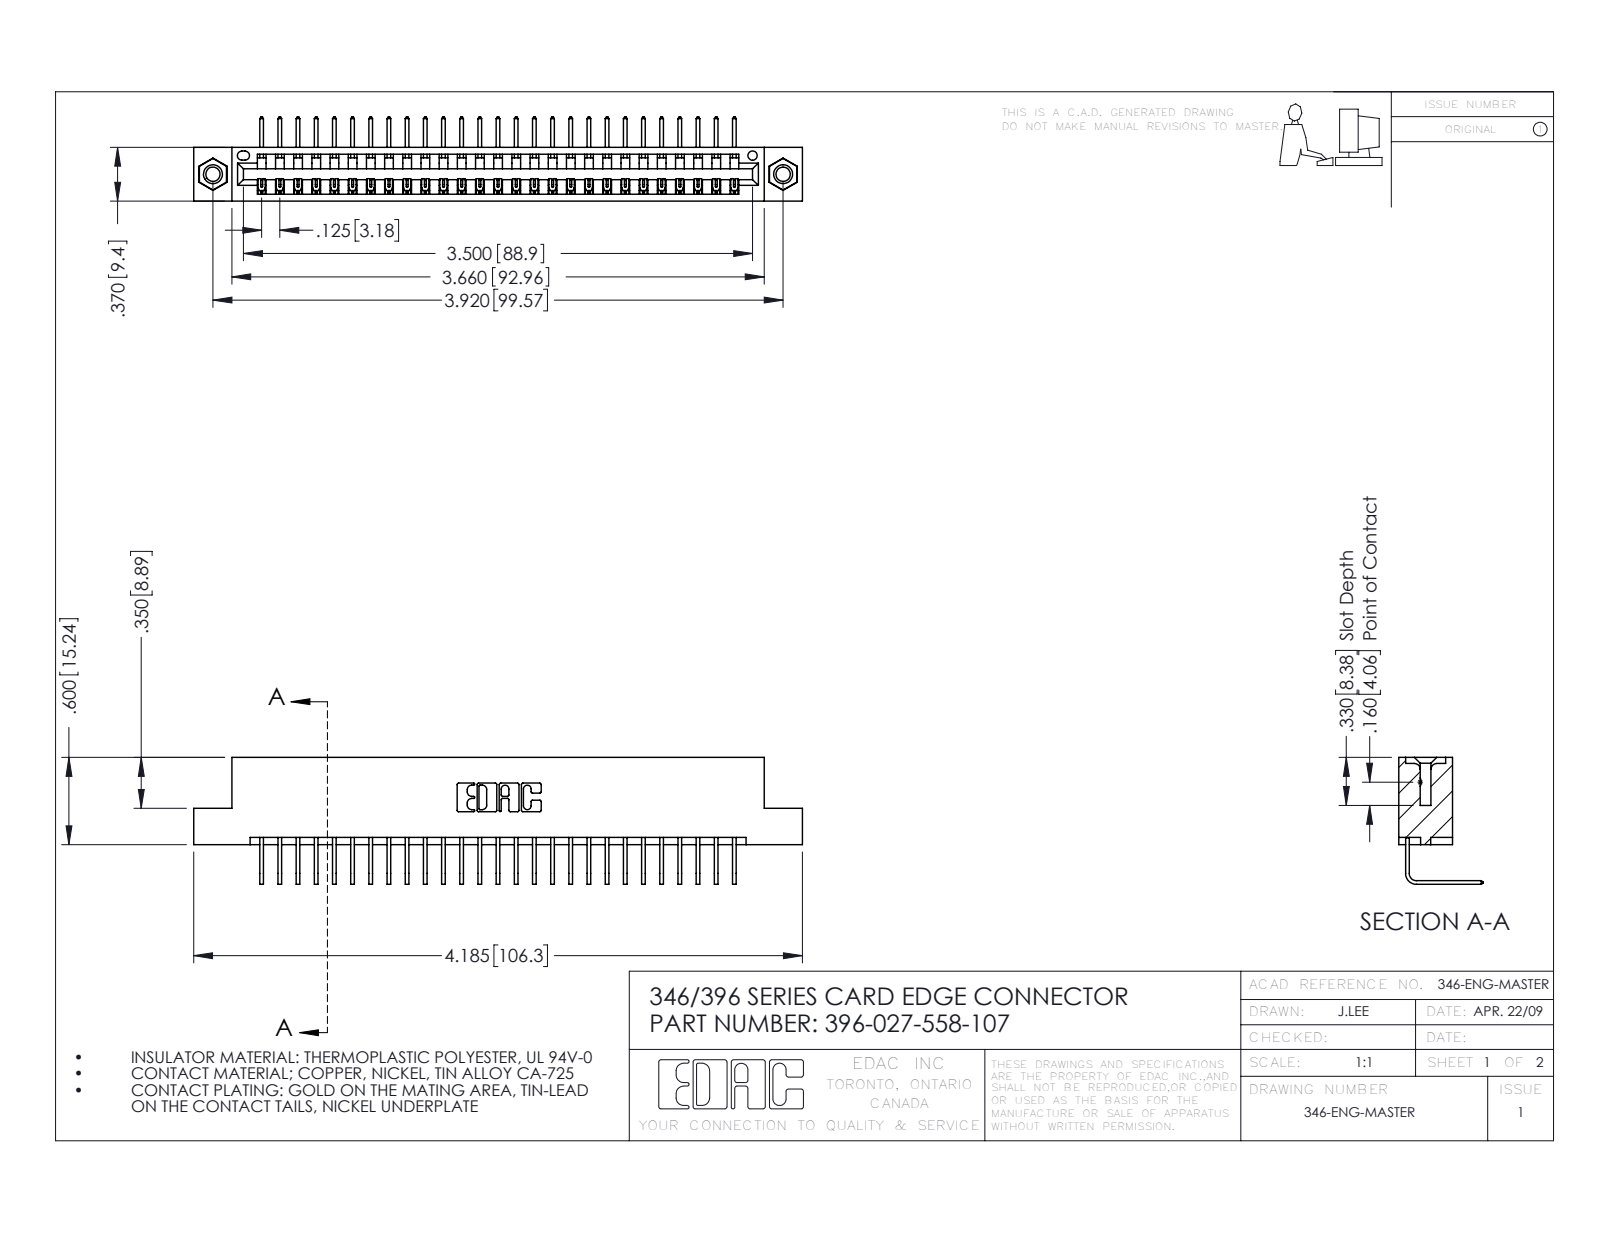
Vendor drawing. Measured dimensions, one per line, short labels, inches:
name: 346 Part_Flush Mounting Lugs - 0.156 Dia-TI; 345-250-001_345-250-005-103; 396-027-558-107; 345-292-001_558 Tail - 2
written by: SolidWorks 2016 (CONFIG_CONTROL_DESIGN)
unit: in
bodies: 30 solids, 1802 faces (1242 planar, 544 cylindrical, 16 other)
size: 4.185 × 0.873 × 0.58
volume: 0.619 in³; area: 20.29 in²
holes: 2× ⌀0.098, 2× ⌀0.125, 2× ⌀0.156, 1× ⌀0.064
bosses: 2× ⌀0.155
rounds: 54× R0.006, 22× R0.01, 6× R0.007, 6× R0.031, 3× R0.026, 2× R0.031, 2× R0.04, 1× R0.014
face distances: 0.322, 0.048, 0.37, 0.25, 0.298, 0.025, 0.072, 0.148, 0.222, 0.1
hole spacings: 0.246, 3.712, 3.92
